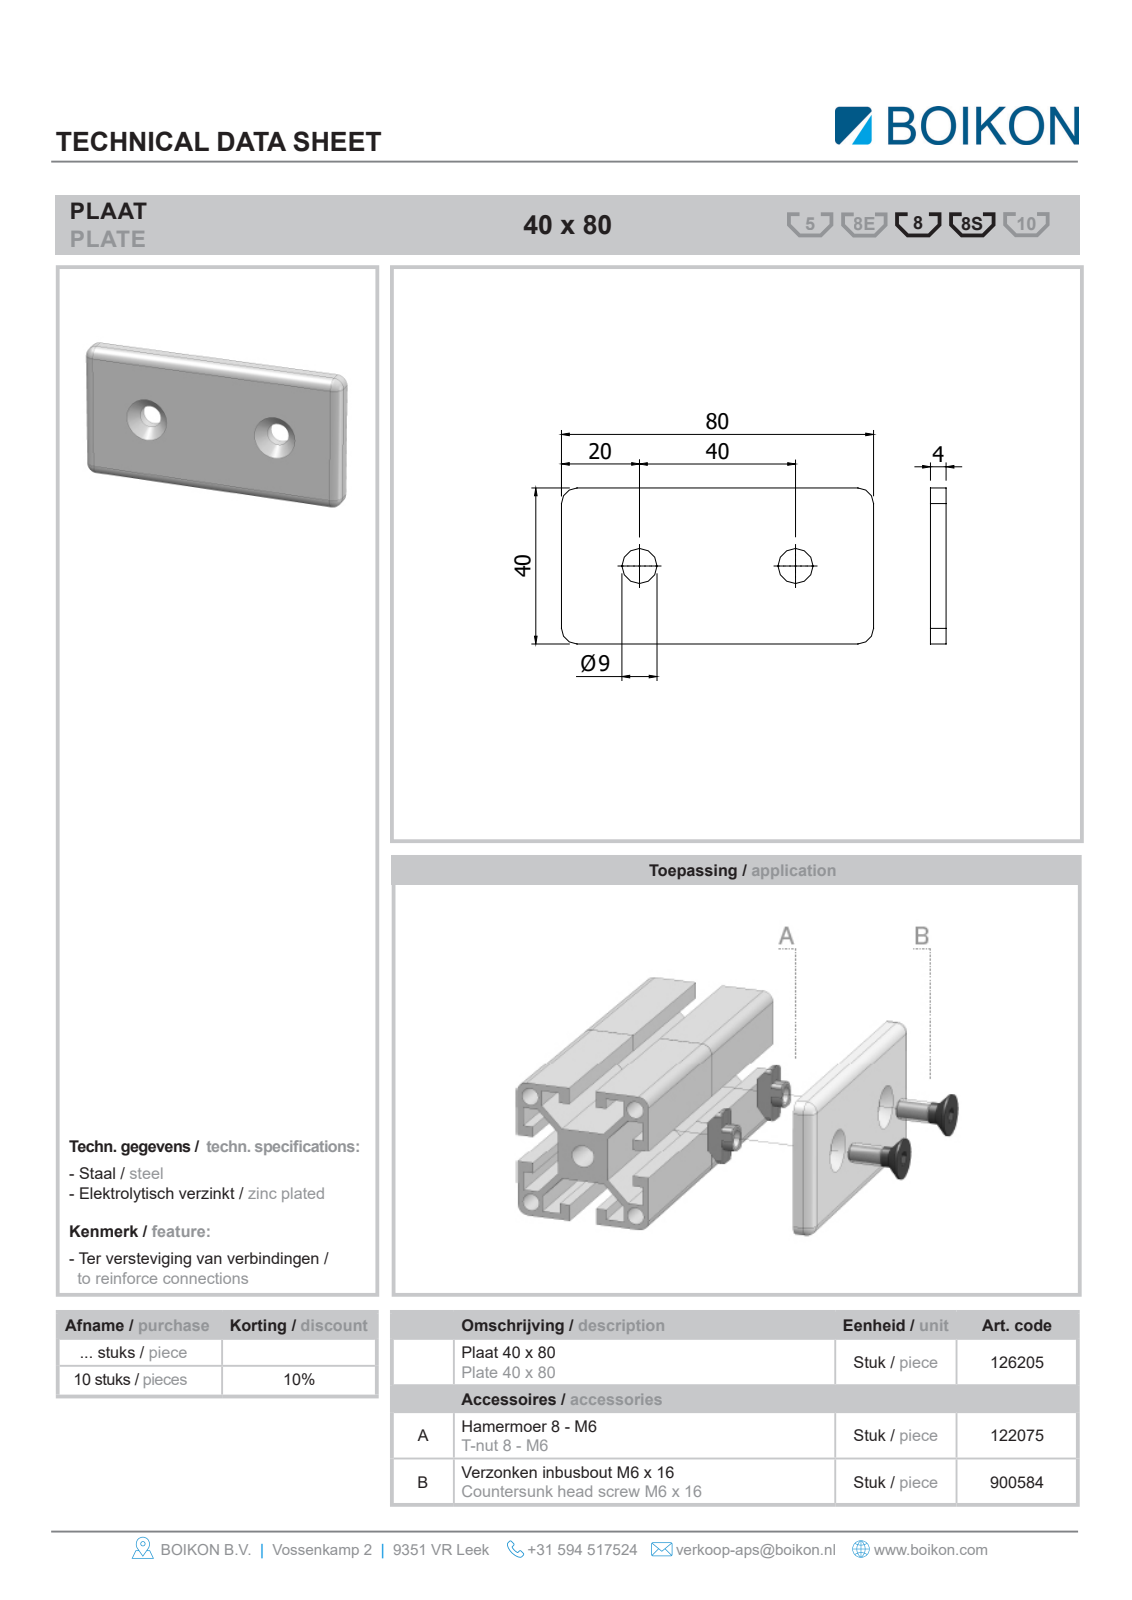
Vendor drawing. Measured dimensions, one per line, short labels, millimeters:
name: Root; 126205Plaat 40 x 80BOIKON; 900584Verz. inbusbout DIN 7991 EV M6 x 16BOIKON0; 122075Hamermoer 8 - M6BOIKON
written by: HiCAD 2013 1802.4 Build 509 (AUTOMOTIVE_DESIGN)
unit: mm
bodies: 5 solids, 160 faces (108 planar, 38 cylindrical, 14 other)
size: 80 × 40 × 16
volume: 19 840 mm³; area: 9 738 mm²
holes: 2× ⌀6, 2× ⌀6.6
bosses: 2× ⌀12, 2× ⌀4.77
rounds: 10× R1, 8× R3, 4× R4, 2× R1.16, 2× R8
face distances: 6, 40, 7.7, 23.85, 16.15, 56.15, 63.85, 0.71, 2.12, 80
hole spacings: 40
